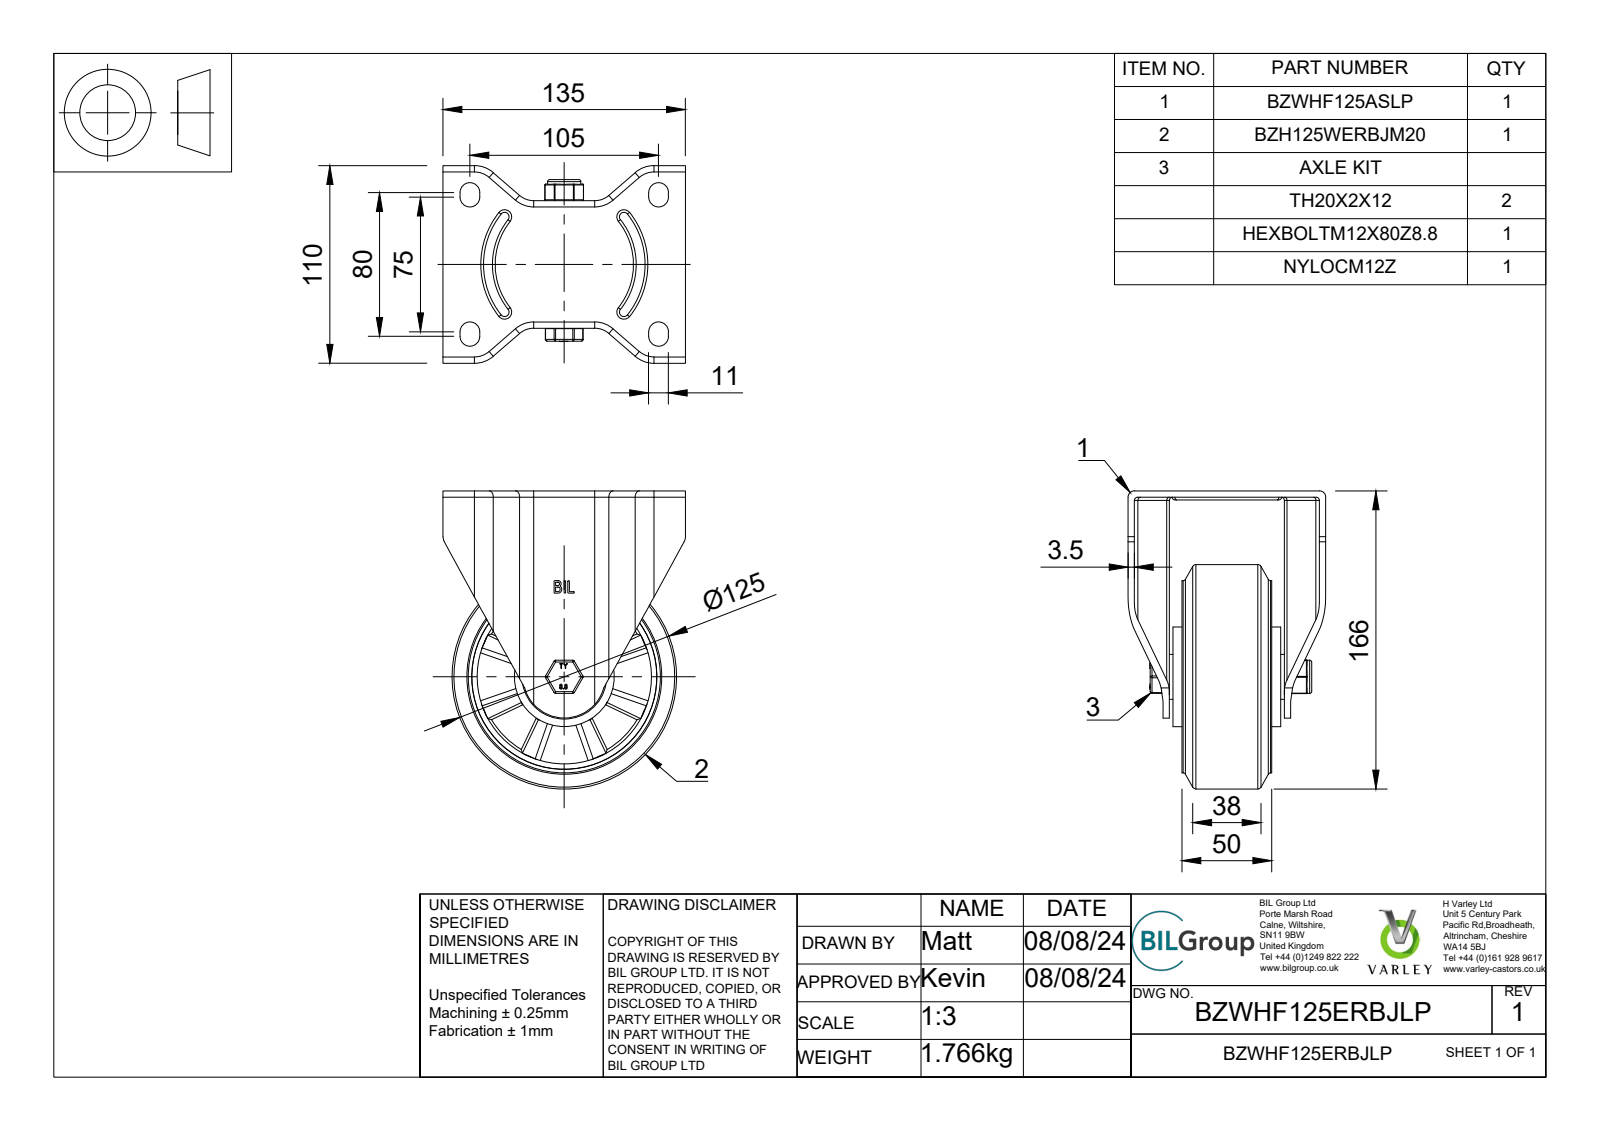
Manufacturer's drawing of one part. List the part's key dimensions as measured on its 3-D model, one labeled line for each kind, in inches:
Part name (STEP PRODUCT): BZWHF125ERBJLP v3; BZWHF125ASLP - 64 v1; ZINC PLATED, PRESSED STEEL BRACKET; BZH125WERBJM20 v1 (+8 more)
STEP written by: Autodesk Translation Framework v13.14.0.145 (AUTOMOTIVE_DESIGN)
Units: inches
Bodies: 35 solids, 1455 faces (620 planar, 296 cylindrical, 539 other)
Overall size (bounding box): 6.535 × 5.315 × 4.331
Volume: 30.89 in³ · Surface area: 369 in²
Round holes (diameter × count): ⌀0.472 ×1, ⌀0.48 ×1, ⌀0.484 ×1, ⌀0.551 ×1, ⌀0.787 ×1, ⌀0.866 ×1, ⌀1.122 ×1, ⌀1.634 ×1, ⌀1.654 ×1, ⌀1.732 ×1, ⌀1.85 ×1, ⌀3.819 ×1
Round bosses / shafts (diameter × count): ⌀4.921 ×1, ⌀4.213 ×1, ⌀2.185 ×1, ⌀1.594 ×1, ⌀1.575 ×1, ⌀1.142 ×1, ⌀1.063 ×1, ⌀0.984 ×1
Partial cylindrical surfaces — rounded edges, fillets, slot ends (radius × count): R0.02 ×18, R0.236 ×18, R0.039 ×12, R0.157 ×12, R0.069 ×8, R0.138 ×8, R0.217 ×8, R0.315 ×4
Main face-to-face distances: 0.138, 0.768, 2.657, 0.63, 2.795, 0.867, 2.028, 1.89, 3.425, 2.52
